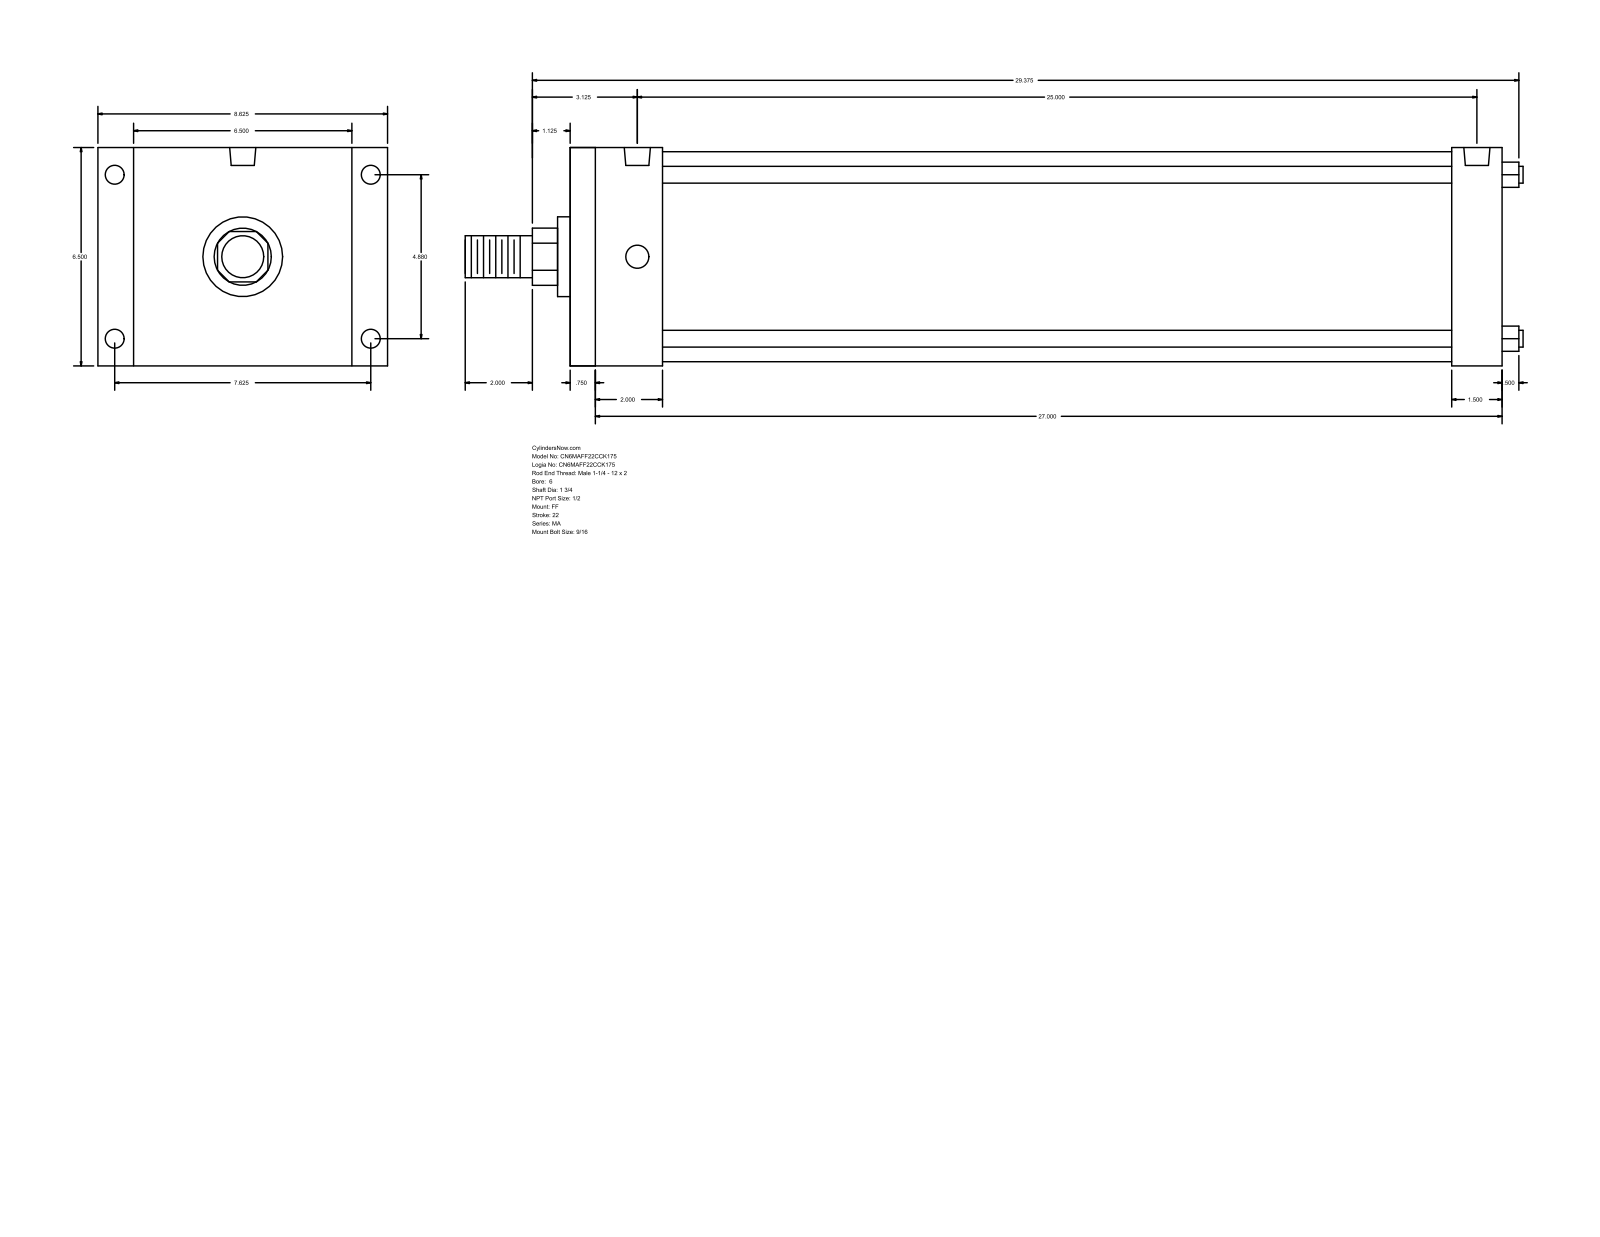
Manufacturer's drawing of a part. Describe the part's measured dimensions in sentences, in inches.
The part is named "MA_FF__0600_1.75". Its 3-D file was written by "GSSL Pune (CONFIG_CONTROL_DESIGN)". It is 0 solids with 92 faces: 64 planar, 28 cylindrical and 0 other. Overall it measures 31.5 by 8.625 by 6.5 inches. Round holes: 4 of diameter 0.563, 4 of diameter 0.687, 2 of diameter 0.778. Round bosses or shafts: 4 of diameter 0.5, 1 of diameter 6.25, 1 of diameter 2.375, 1 of diameter 1.75, 1 of diameter 1.25. Partial cylindrical surfaces (rounded edges, fillets, slot ends): 1 of radius 0.852. The main face-to-face distances are 6.5, 27.75, 0.75, 27, 2.75, 2, 25, 26.25, 25.5, 23.5. The hole center spacings are 4.88, 7.625, 9.053, 25.
